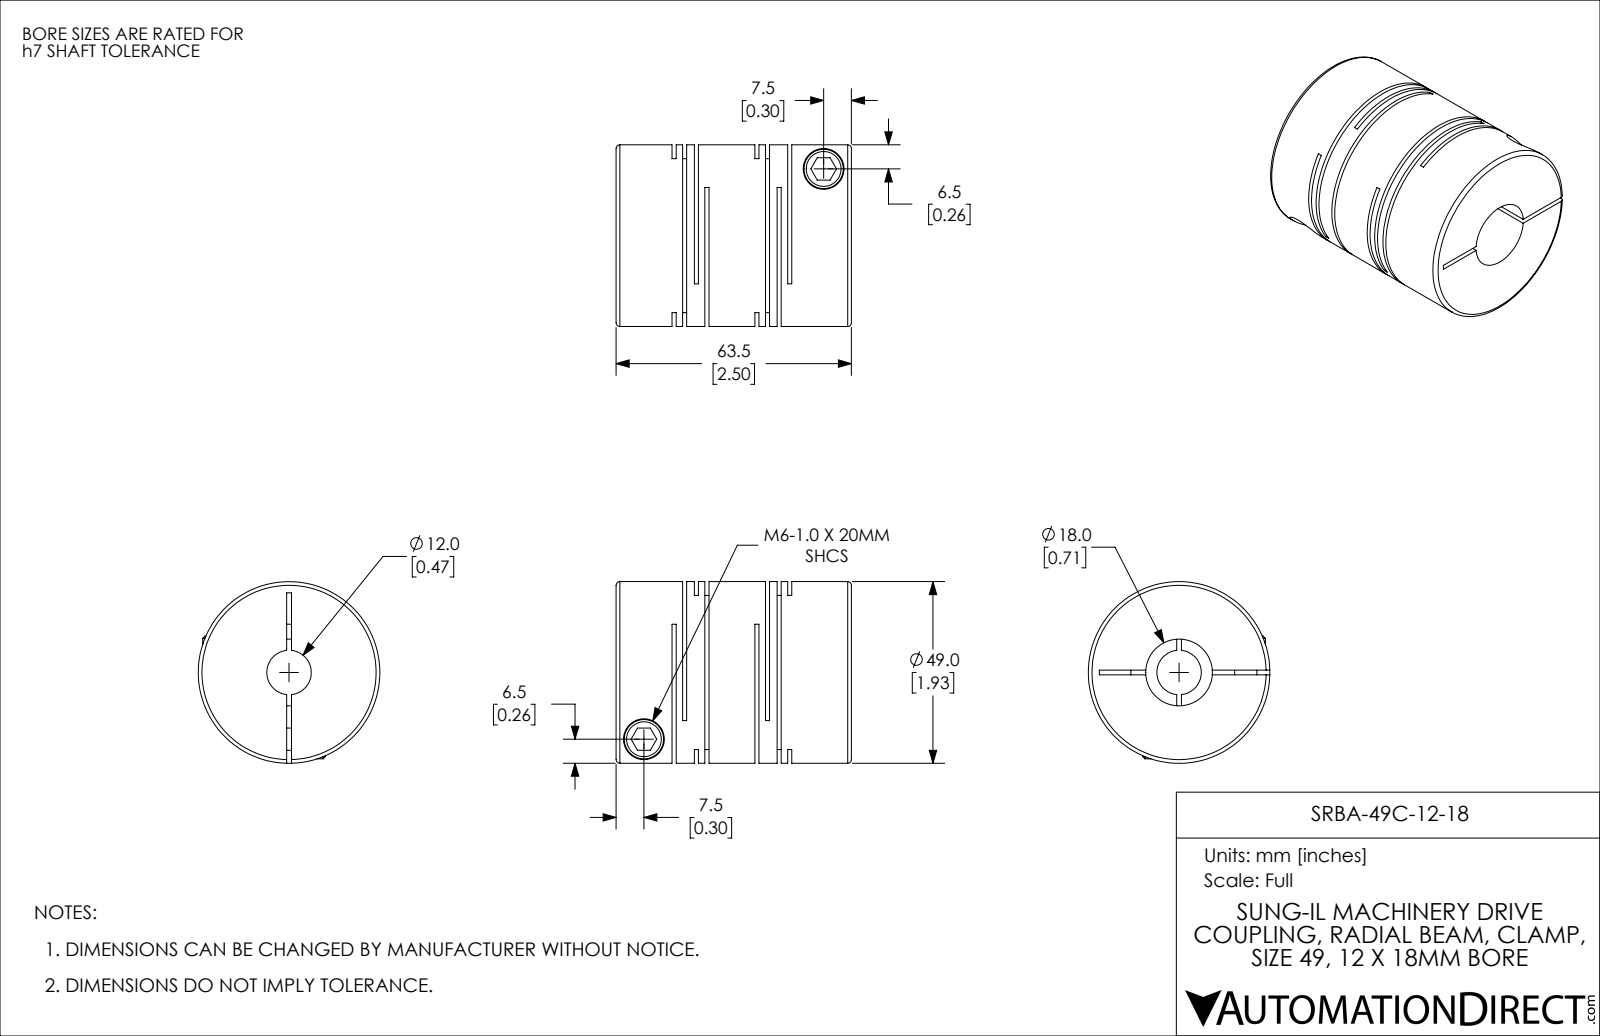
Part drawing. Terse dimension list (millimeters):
name: SRBA-49C-12-18
written by: SolidWorks 2021 (CONFIG_CONTROL_DESIGN)
unit: mm
bodies: 1 solid, 114 faces (60 planar, 42 cylindrical, 12 other)
size: 63.5 × 49 × 49
volume: 91 430 mm³; area: 38 978 mm²
holes: 2× ⌀6, 2× ⌀11, 1× ⌀12, 1× ⌀18
bosses: 2× ⌀10.6, 1× ⌀49
face distances: 6, 1.1, 2.85, 22.35, 4.9, 21.25, 3.15, 19.5, 16.35, 1.75
